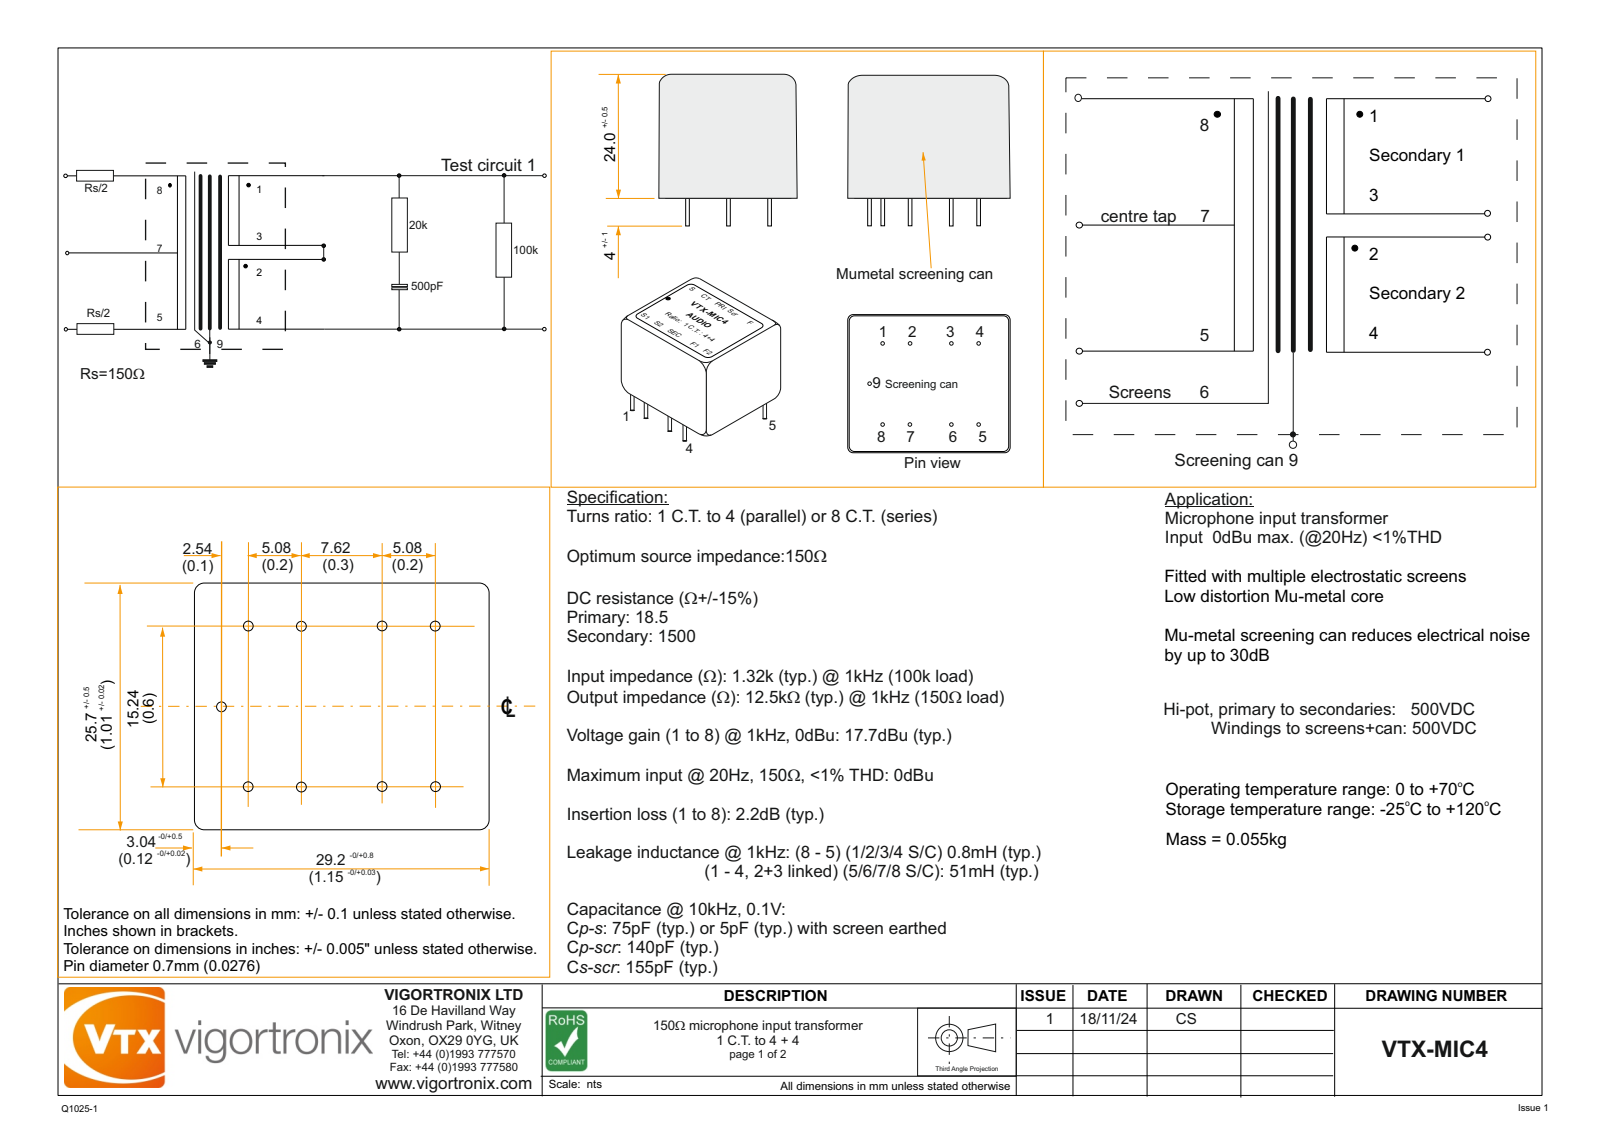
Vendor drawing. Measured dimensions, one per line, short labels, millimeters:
name: VTX-MIC4 BOBBIN; VTX-MIC4; VTX-MIC4 CAN; VTX-MIC4 LID
written by: SolidWorks 2024 (AUTOMOTIVE_DESIGN)
unit: mm
bodies: 3 solids, 130 faces (36 planar, 74 cylindrical, 20 other)
size: 29.62 × 28.6 × 25.22
volume: 15 314 mm³; area: 10 856 mm²
holes: 8× ⌀3.5, 1× ⌀1.5
bosses: 8× ⌀0.7
rounds: 20× R0.5, 8× R1.9, 8× R2.5, 4× R2
face distances: 0.6, 23.4, 22.8, 22.5, 0.9, 23.1, 24, 23, 27.5, 2.6
hole spacings: 5.08, 12.7, 15.24, 16.06, 17.04, 19.84, 7.62, 8.03
